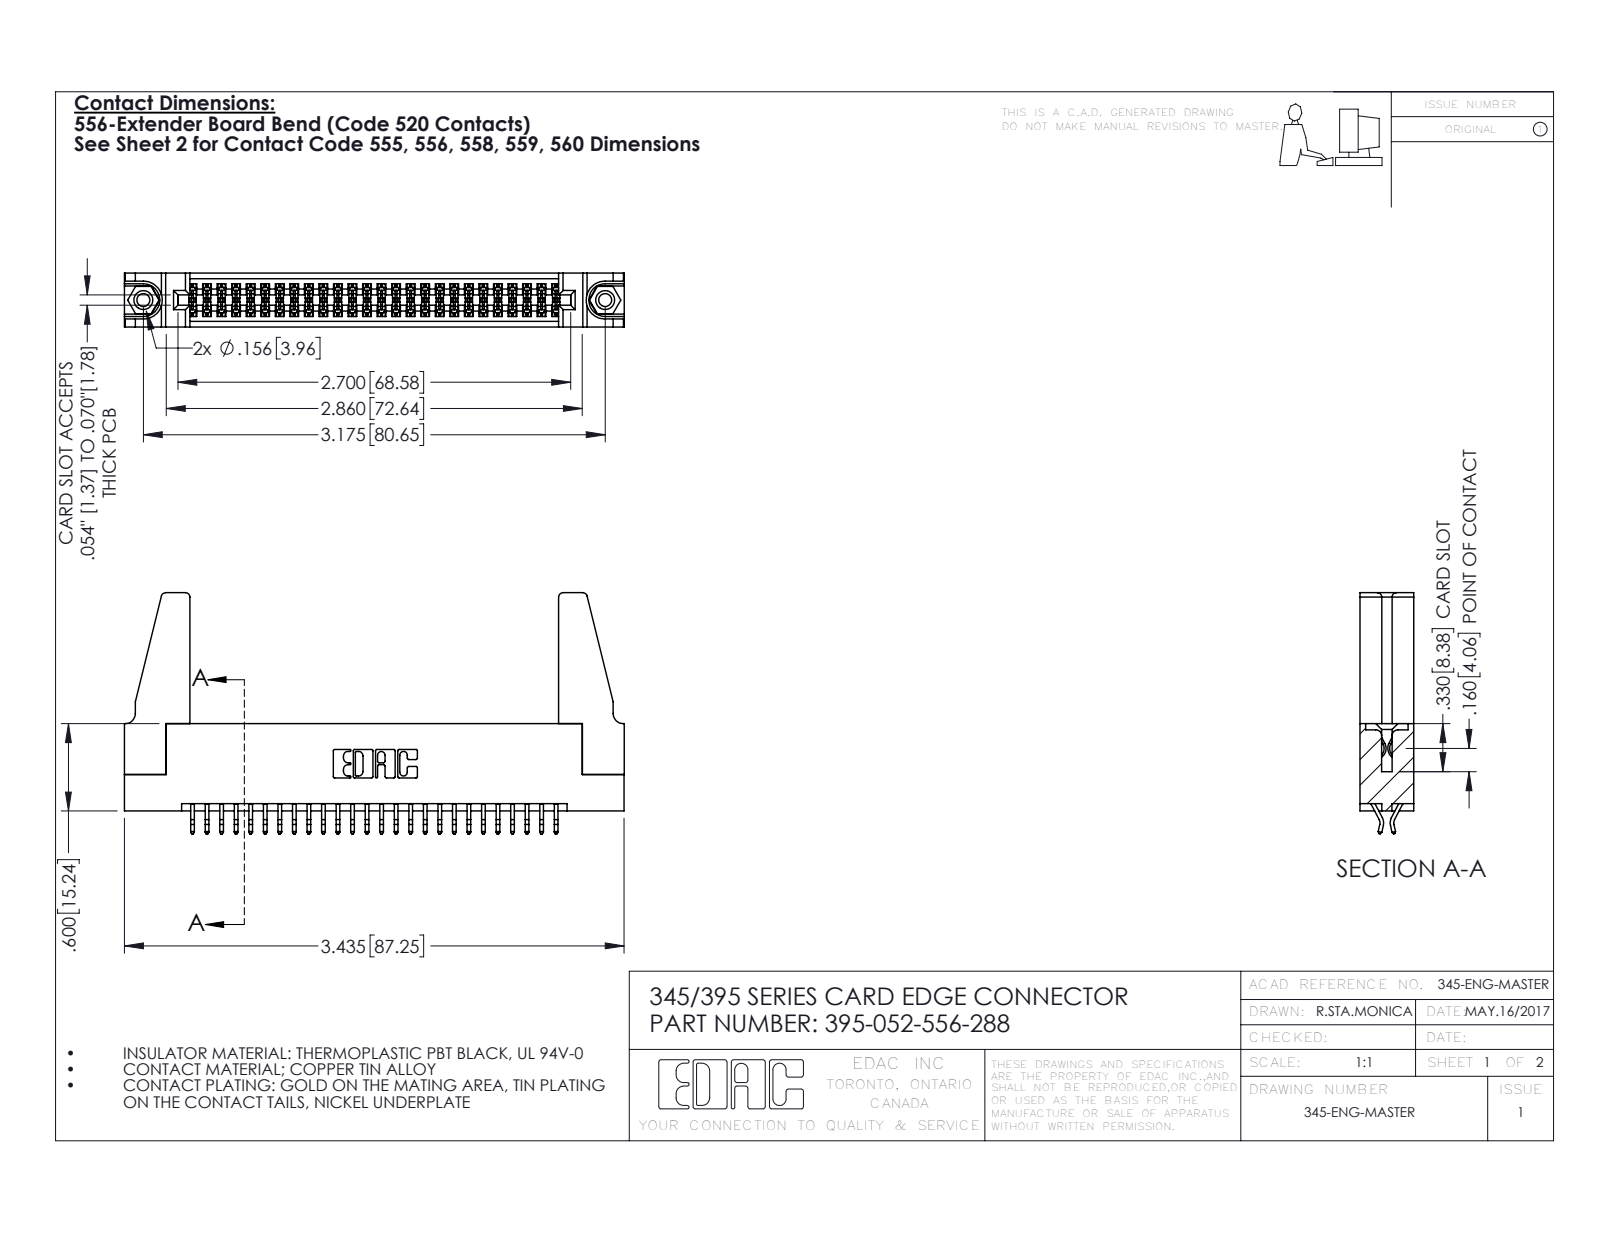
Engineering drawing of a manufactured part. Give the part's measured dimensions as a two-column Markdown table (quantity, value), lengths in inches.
| quantity | value |
| --- | --- |
| part name | 345-292-001_556 Tail; 345-250-001_345-250-001-102; 395-052-556-288; 345 Part_Flush Mounting Lugs - 0.156 Dia-TH (+1 more) |
| STEP written by | SolidWorks 2016 (CONFIG_CONTROL_DESIGN) |
| units | inches |
| bodies | 57 solids, 3162 faces (2076 planar, 1070 cylindrical, 16 other) |
| overall size | 3.436 × 1.657 × 0.37 |
| volume | 0.707 in³ |
| surface area | 23.37 in² |
| round holes (diameter × count) | 0.089 × 2, 0.125 × 2, 0.156 × 2, 0.064 × 1 |
| round bosses / shafts (diameter × count) | 0.155 × 2 |
| partial cylindrical surfaces (radius × count) | 0.006 × 78, 0.01 × 22, 0.03 × 8, 0.007 × 6, 0.031 × 6, 0.026 × 3, 0.01 × 2, 0.014 × 2 |
| main face-to-face distances | 0.072, 0.37, 0.298, 0.2, 0.025, 0.098, 0.272, 0.225, 0.175, 0.149 |
| hole center spacings | 0.27, 2.94, 3.175 |
